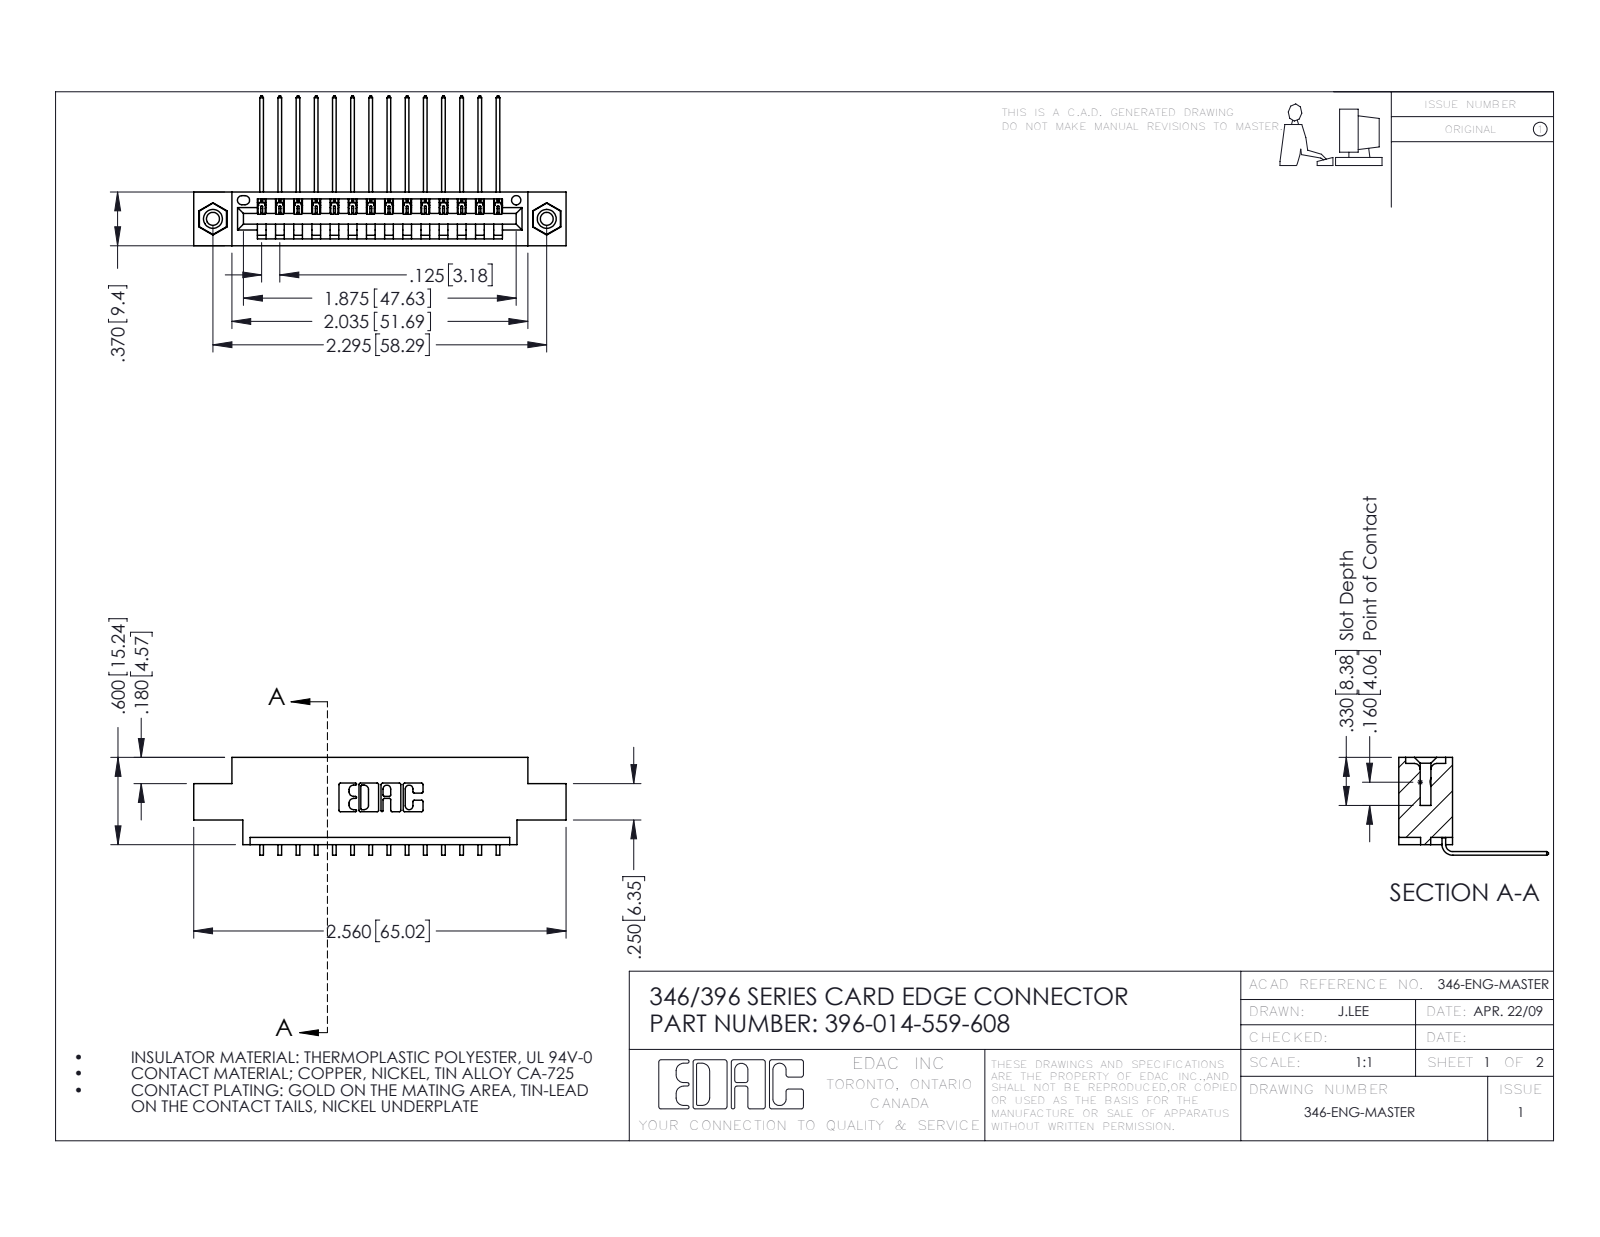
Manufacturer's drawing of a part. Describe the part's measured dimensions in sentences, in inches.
The part is named "345-250-001_345-250-003-102; 345-292-001_558 559 Tail - 1; 396-014-559-608; 346 Part_0.170 Offset - 0.156 Dia-TI". Its 3-D file was written by "SolidWorks 2016 (CONFIG_CONTROL_DESIGN)". It is 17 solids with 1026 faces: 700 planar, 310 cylindrical and 16 other. Overall it measures 2.56 by 1.03 by 0.673 inches. Its volume is 0.361 cubic inches and its surface area 11.71 square inches. Round holes: 2 of diameter 0.089, 2 of diameter 0.125, 2 of diameter 0.156, 1 of diameter 0.064. Round bosses or shafts: 2 of diameter 0.155. Partial cylindrical surfaces (rounded edges, fillets, slot ends): 28 of radius 0.006, 22 of radius 0.01, 6 of radius 0.007, 6 of radius 0.031, 3 of radius 0.026, 2 of radius 0.031, 2 of radius 0.04, 1 of radius 0.014. The main face-to-face distances are 0.048, 0.37, 0.322, 0.25, 0.025, 0.072, 0.222, 0.148, 0.1, 0.174. The hole center spacings are 0.246, 2.089, 2.295.
